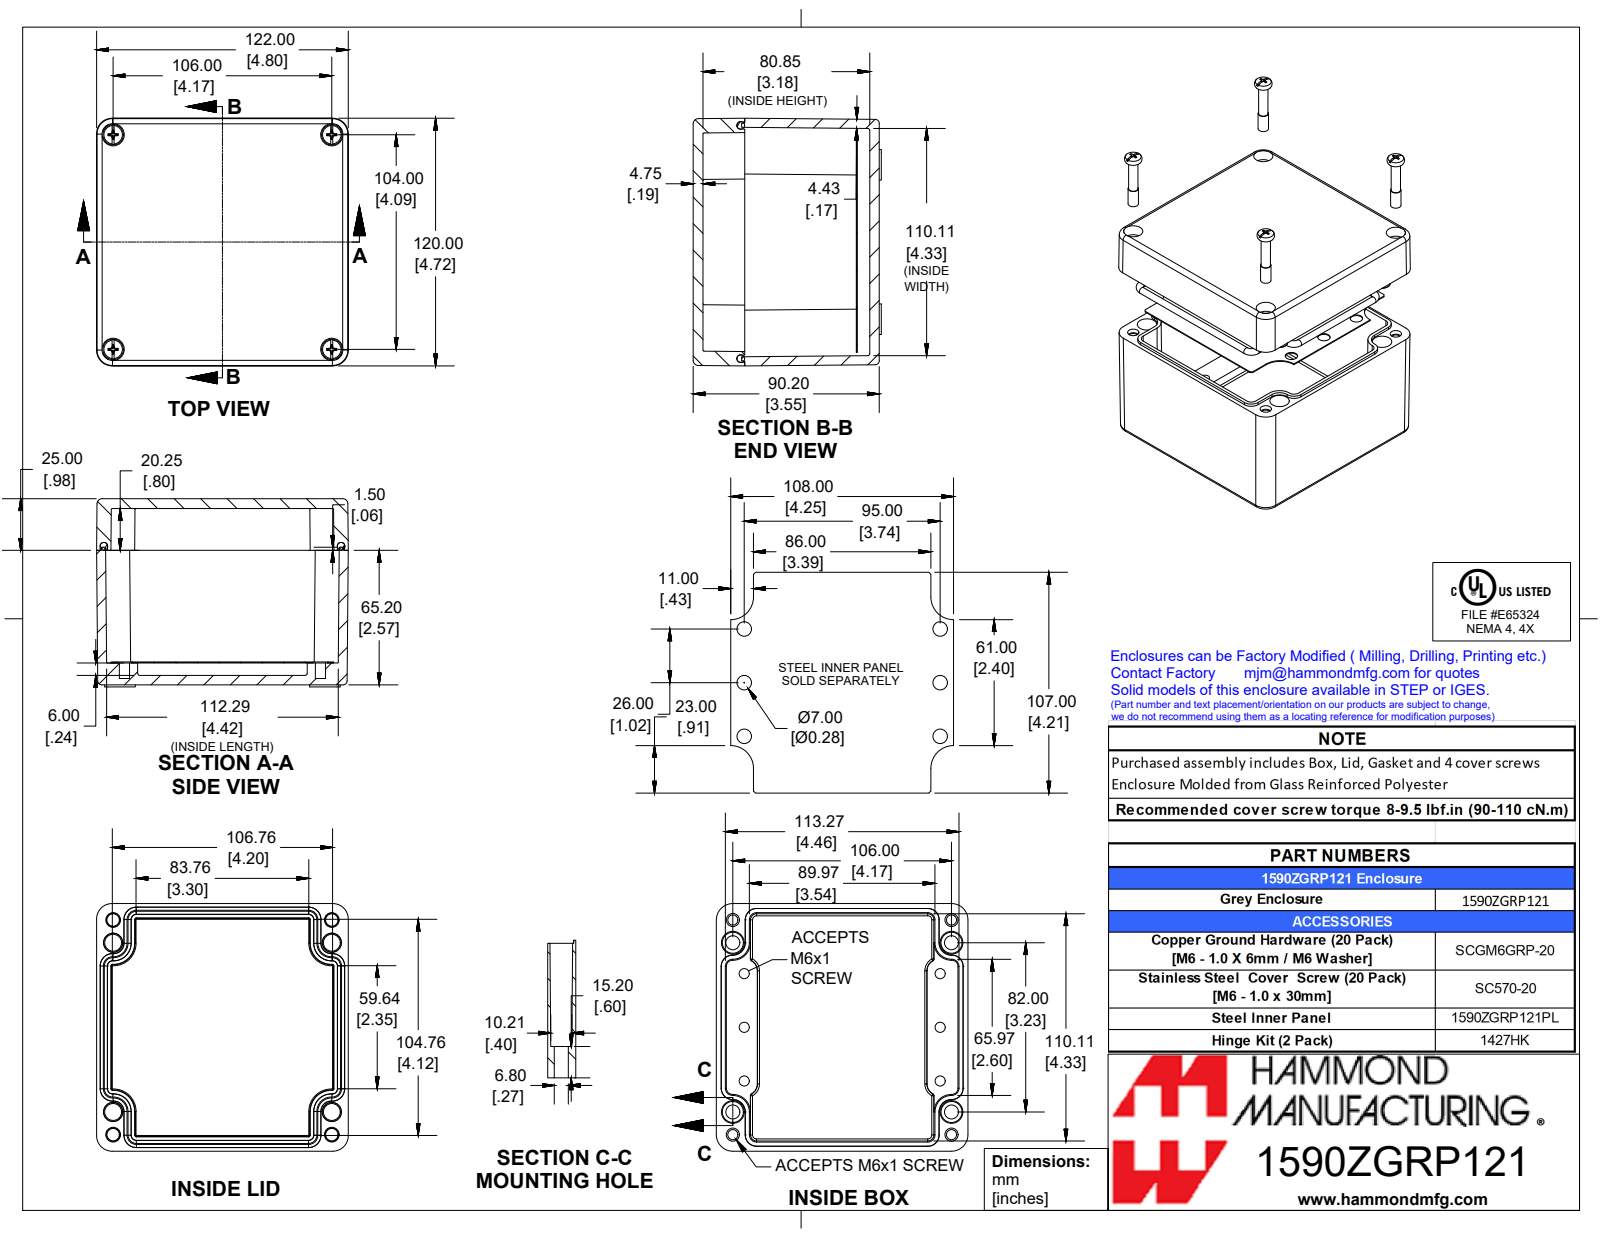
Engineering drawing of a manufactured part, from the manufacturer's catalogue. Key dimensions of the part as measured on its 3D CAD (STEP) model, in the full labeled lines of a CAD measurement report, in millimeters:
Part name (STEP PRODUCT): 1590ZGRP121
STEP written by: SolidWorks 2019 (CONFIG_CONTROL_DESIGN)
Units: millimetres
Bodies: 8 solids, 521 faces (233 planar, 108 cylindrical, 180 other)
Overall size (bounding box): 122 × 120 × 91.2
Volume: 394 300 mm³ · Surface area: 178 000 mm²
Round holes (diameter × count): ⌀4.9 ×10, ⌀7 ×6, ⌀6 ×4, ⌀6.4 ×4, ⌀6.8 ×4, ⌀10.8 ×4
Round bosses / shafts (diameter × count): ⌀3.8 ×6, ⌀5.9 ×4, ⌀5.3 ×4
Partial cylindrical surfaces — rounded edges, fillets, slot ends (radius × count): R1.5 ×20, R0.5 ×6, R1 ×6, R2 ×4, R2.5 ×4, R7.5 ×4, R8 ×4, R11 ×4
Main face-to-face distances: 90.2, 10.6, 79.6, 0.5, 11.1, 79.1, 85.4, 74.9, 74.3, 4.7
Hole centre spacings: 11, 16, 26, 26.6, 41.4, 52.3, 67.2, 78.2
